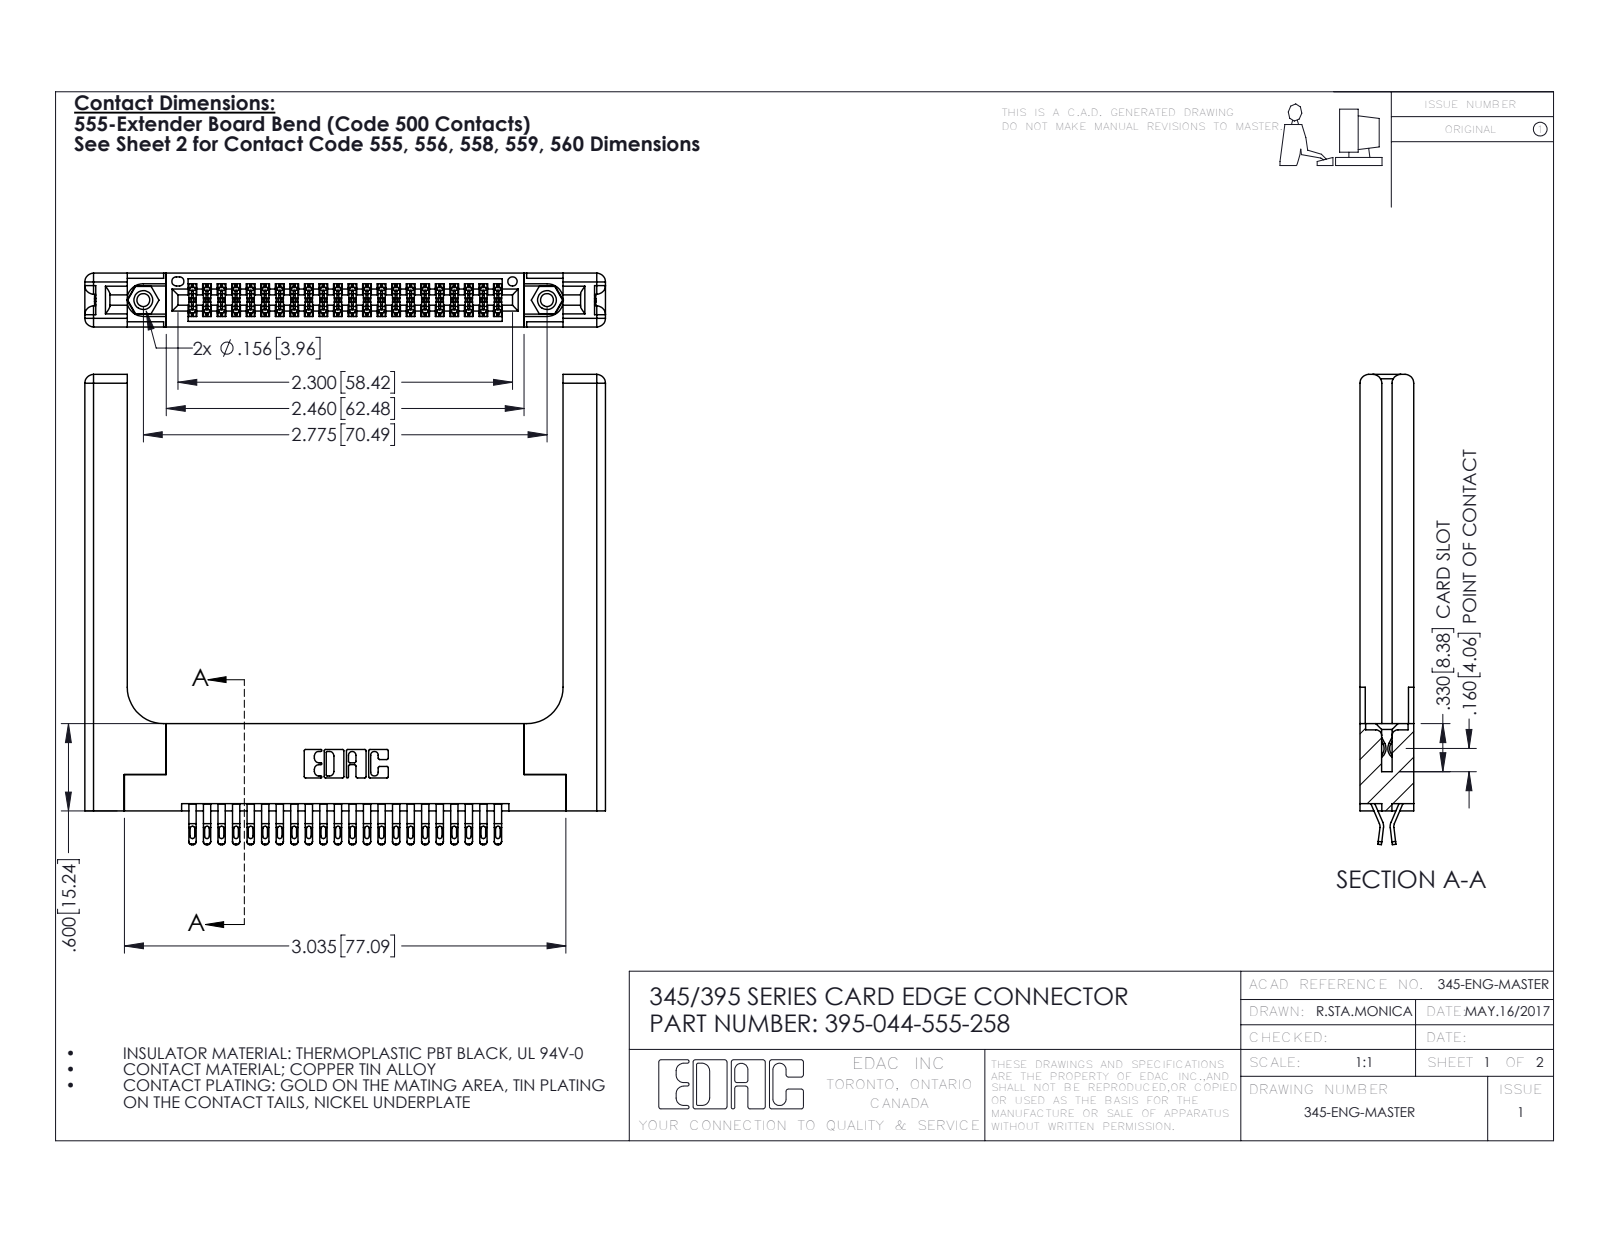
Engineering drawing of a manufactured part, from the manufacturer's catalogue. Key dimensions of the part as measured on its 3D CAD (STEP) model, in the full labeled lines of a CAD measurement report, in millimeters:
Part name (STEP PRODUCT): 345-292-001_555 Tail; 345-220-058_345-220-058; 395-044-555-258; 345-250-001_345-250-001-102 (+1 more)
STEP written by: SolidWorks 2016 (CONFIG_CONTROL_DESIGN)
Units: millimetres
Bodies: 49 solids, 2846 faces (1592 planar, 1194 cylindrical, 60 other)
Overall size (bounding box): 90.9 × 82.1 × 9.4
Volume: 17 260 mm³ · Surface area: 18 080 mm²
Round holes (diameter × count): ⌀2.3 ×2, ⌀3.2 ×2, ⌀4 ×2, ⌀1.6 ×1
Round bosses / shafts (diameter × count): ⌀3.9 ×2
Partial cylindrical surfaces — rounded edges, fillets, slot ends (radius × count): R0.4 ×110, R0.5 ×88, R0.2 ×66, R0.3 ×22, R1.5 ×16, R0.2 ×6, R0.8 ×6, R0.7 ×3
Main face-to-face distances: 9.4, 1.8, 7.6, 5.1, 0.6, 3.8, 3.8, 2, 5.7, 5.6
Hole centre spacings: 6.9, 64.5, 70.5
